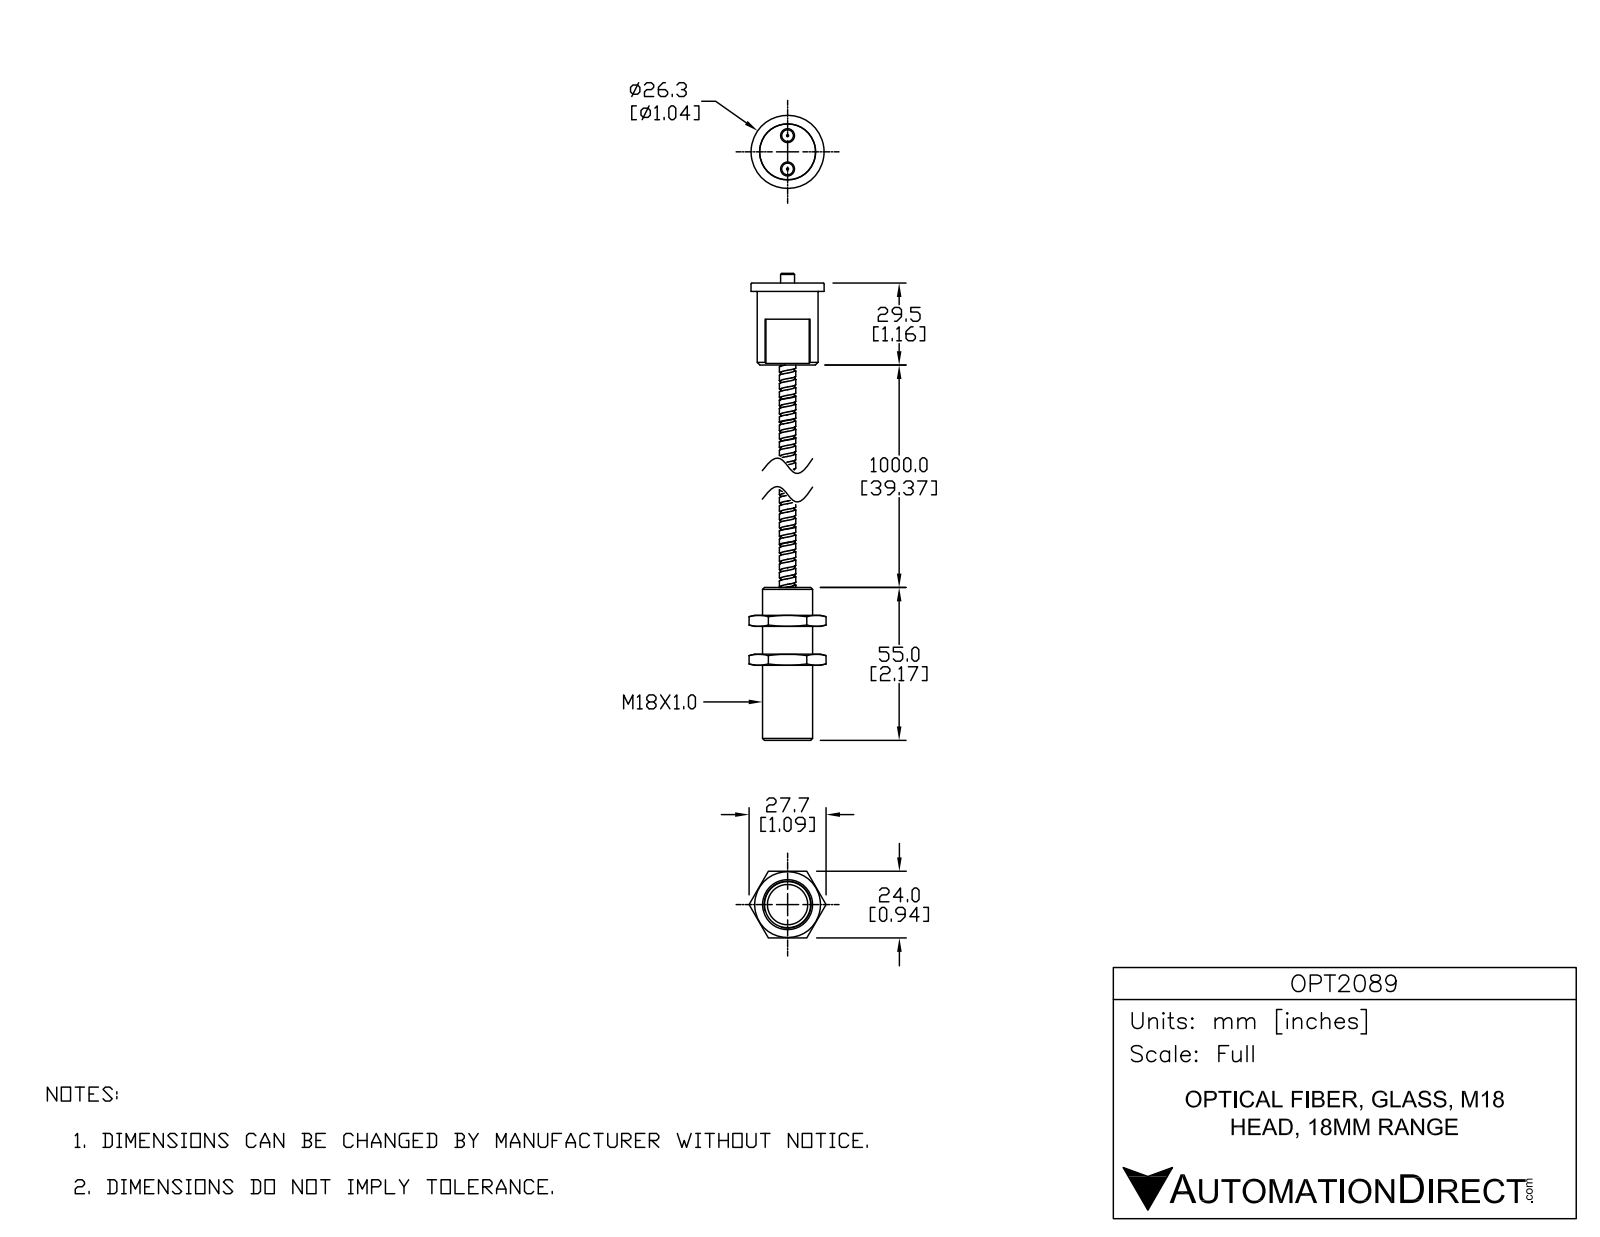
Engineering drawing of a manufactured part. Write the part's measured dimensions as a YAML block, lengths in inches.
part_name: "ZNR11011"
step_written_by: "Unknown (AUTOMOTIVE_DESIGN)"
units: inches
bodies: {solids: 2, faces: 85, planar: 33, cylindrical: 29, other: 23}
overall_size: [6.614, 1.091, 1.035]
volume: 1.789
surface_area: 15.32
round_holes:
  - {diameter: 0.03, count: 2}
  - {diameter: 0.571, count: 1}
  - {diameter: 0.793, count: 1}
round_bosses_or_shafts:
  - {diameter: 0.197, count: 2}
  - {diameter: 1.035, count: 1}
  - {diameter: 0.862, count: 1}
  - {diameter: 0.791, count: 1}
  - {diameter: 0.783, count: 1}
  - {diameter: 0.709, count: 1}
  - {diameter: 0.232, count: 1}
partial_cylinders:
  - {radius: 0.415, count: 1}
face_to_face_distances: [0.551, 0.945, 0.394, 0.157, 1.161, 3.15, 4.311, 4.094, 5.256, 1.102]
hole_center_spacings: [0.23, 0.242, 0.472]
